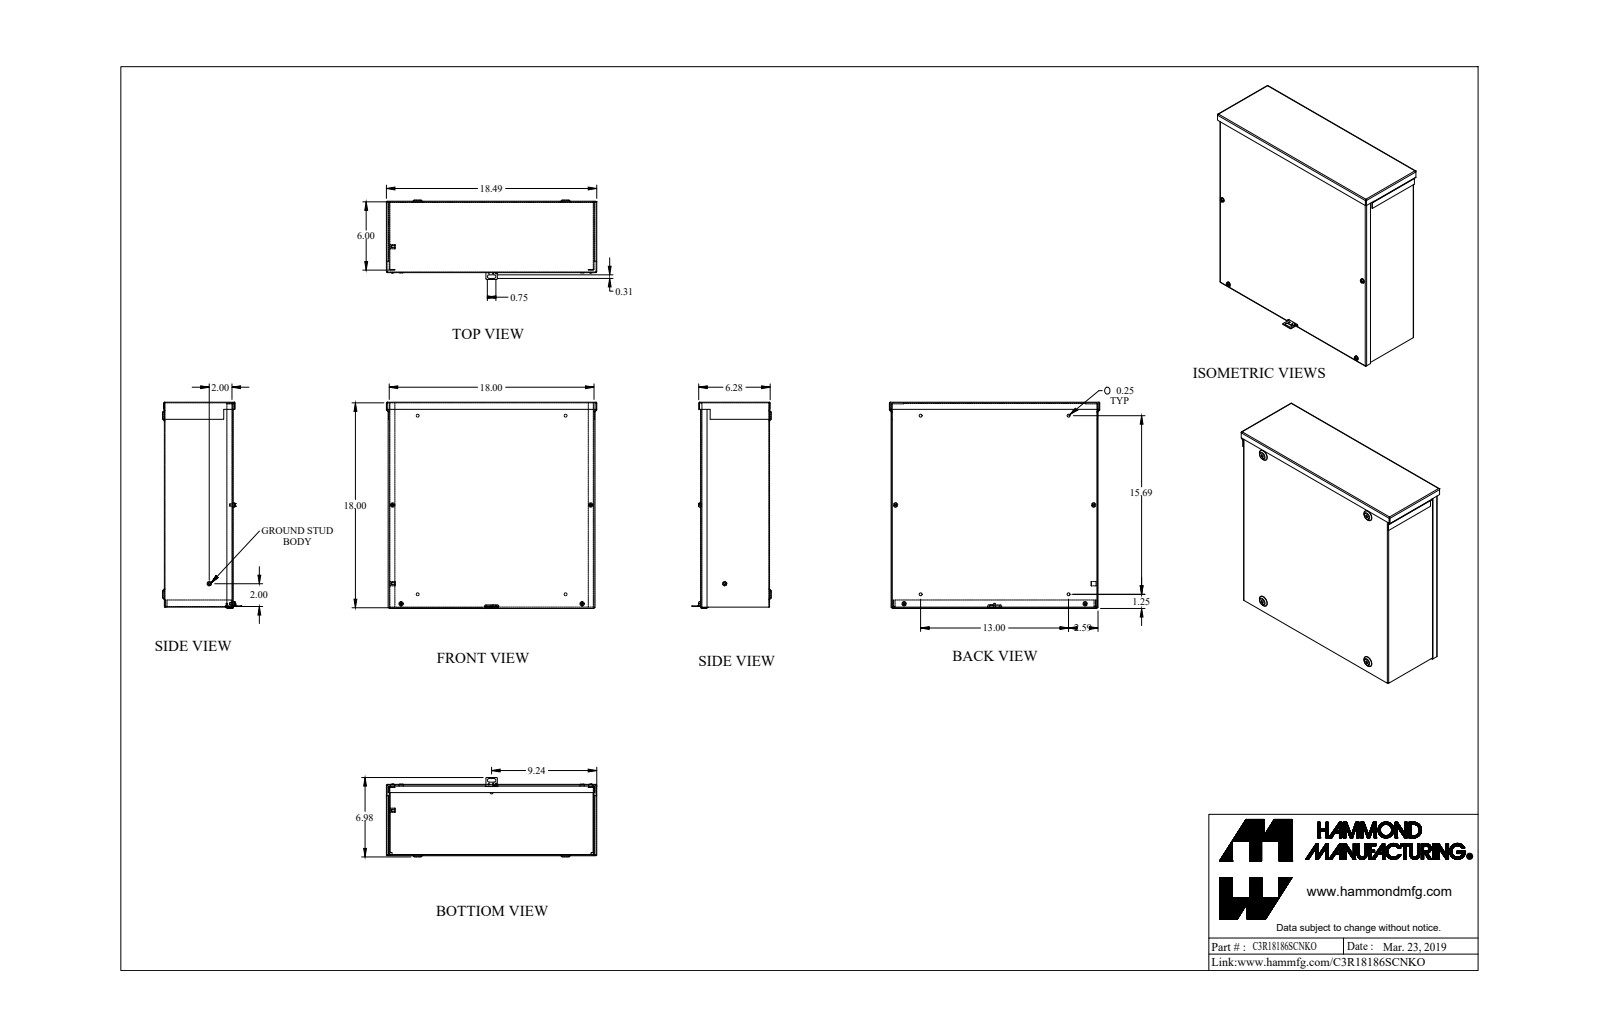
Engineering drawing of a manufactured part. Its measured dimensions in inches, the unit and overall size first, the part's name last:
Units: inches
Overall size (bounding box): 18.489 × 18.12 × 6.977
Round holes (diameter × count): ⌀0.17 ×4, ⌀0.25 ×4, ⌀0.125 ×1, ⌀0.137 ×1, ⌀0.156 ×1
Round bosses / shafts (diameter × count): ⌀0.19 ×4, ⌀0.375 ×3, ⌀0.375 ×2, ⌀0.125 ×1
Partial cylindrical surfaces — rounded edges, fillets, slot ends (radius × count): R0.029 ×21, R0.086 ×21, R0.109 ×8, R0.125 ×8, R0.156 ×2
Main face-to-face distances: 0.057, 6, 5.943, 6.057, 17.943, 18, 0.057, 17.886, 17.886, 17.943
Hole centre spacings: 8.151, 17.112, 1.675, 8.711, 13, 14.478, 15.693, 16.589
Volume: 68.19 in³ · Surface area: 2 409 in²
Bodies: 11 solids, 404 faces (211 planar, 107 cylindrical, 86 other)
Part name (STEP PRODUCT): C3R18186SCNKO_Default
STEP written by: SolidWorks 2019 (CONFIG_CONTROL_DESIGN)
